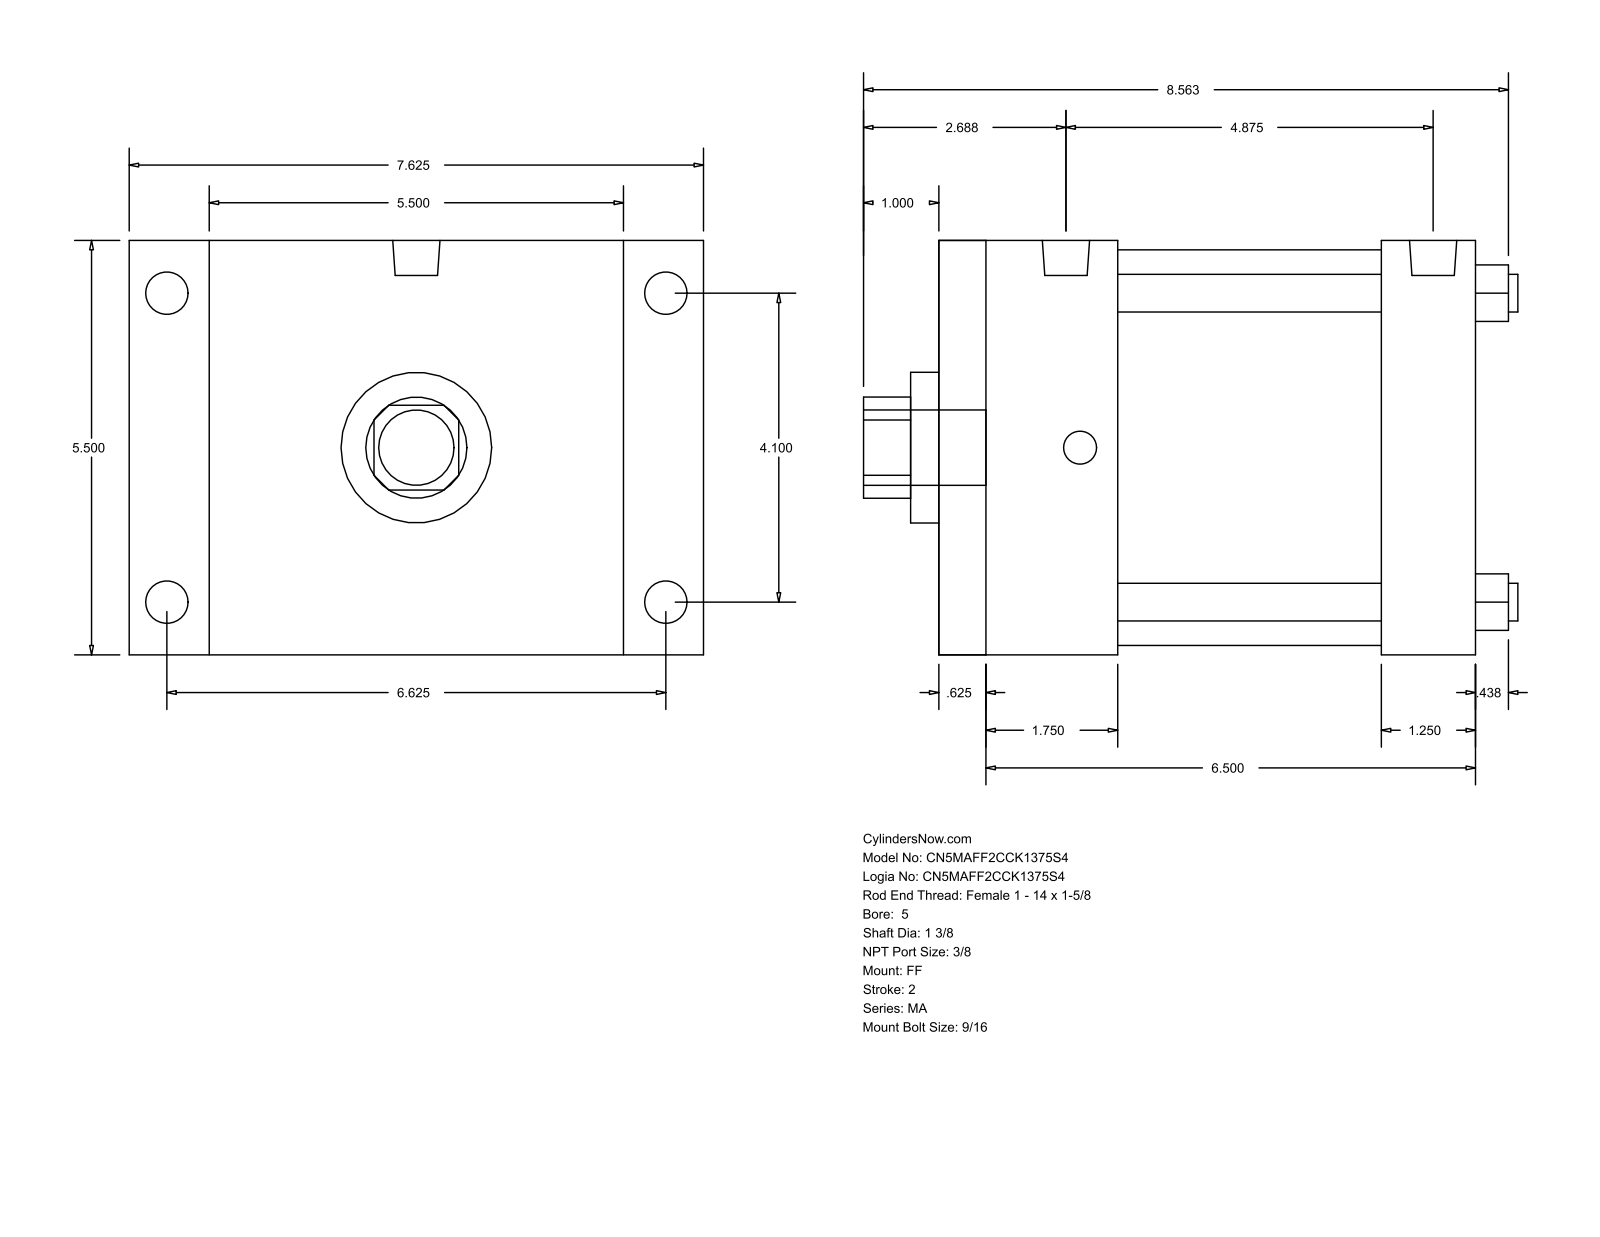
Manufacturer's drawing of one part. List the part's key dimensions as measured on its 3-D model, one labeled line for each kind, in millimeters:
Part name (STEP PRODUCT): MA_FF__0500_1.375
STEP written by: GSSL Pune (CONFIG_CONTROL_DESIGN)
Units: millimetres
Bodies: 0 solids, 92 faces (64 planar, 28 cylindrical, 0 other)
Overall size (bounding box): 220.66 × 193.68 × 139.7
Round holes (diameter × count): ⌀12.7 ×4, ⌀34.92 ×1, ⌀50.8 ×1, ⌀133.35 ×1
Round bosses / shafts (diameter × count): ⌀14.29 ×4, ⌀11.11 ×4, ⌀15.93 ×2, ⌀25.4 ×1
Partial cylindrical surfaces — rounded edges, fillets, slot ends (radius × count): R17.06 ×1
Main face-to-face distances: 139.7, 180.98, 15.87, 165.11, 149.22, 133.35, 31.76, 60.32, 44.45, 88.9
Hole centre spacings: 73.64, 104.14, 147.28
